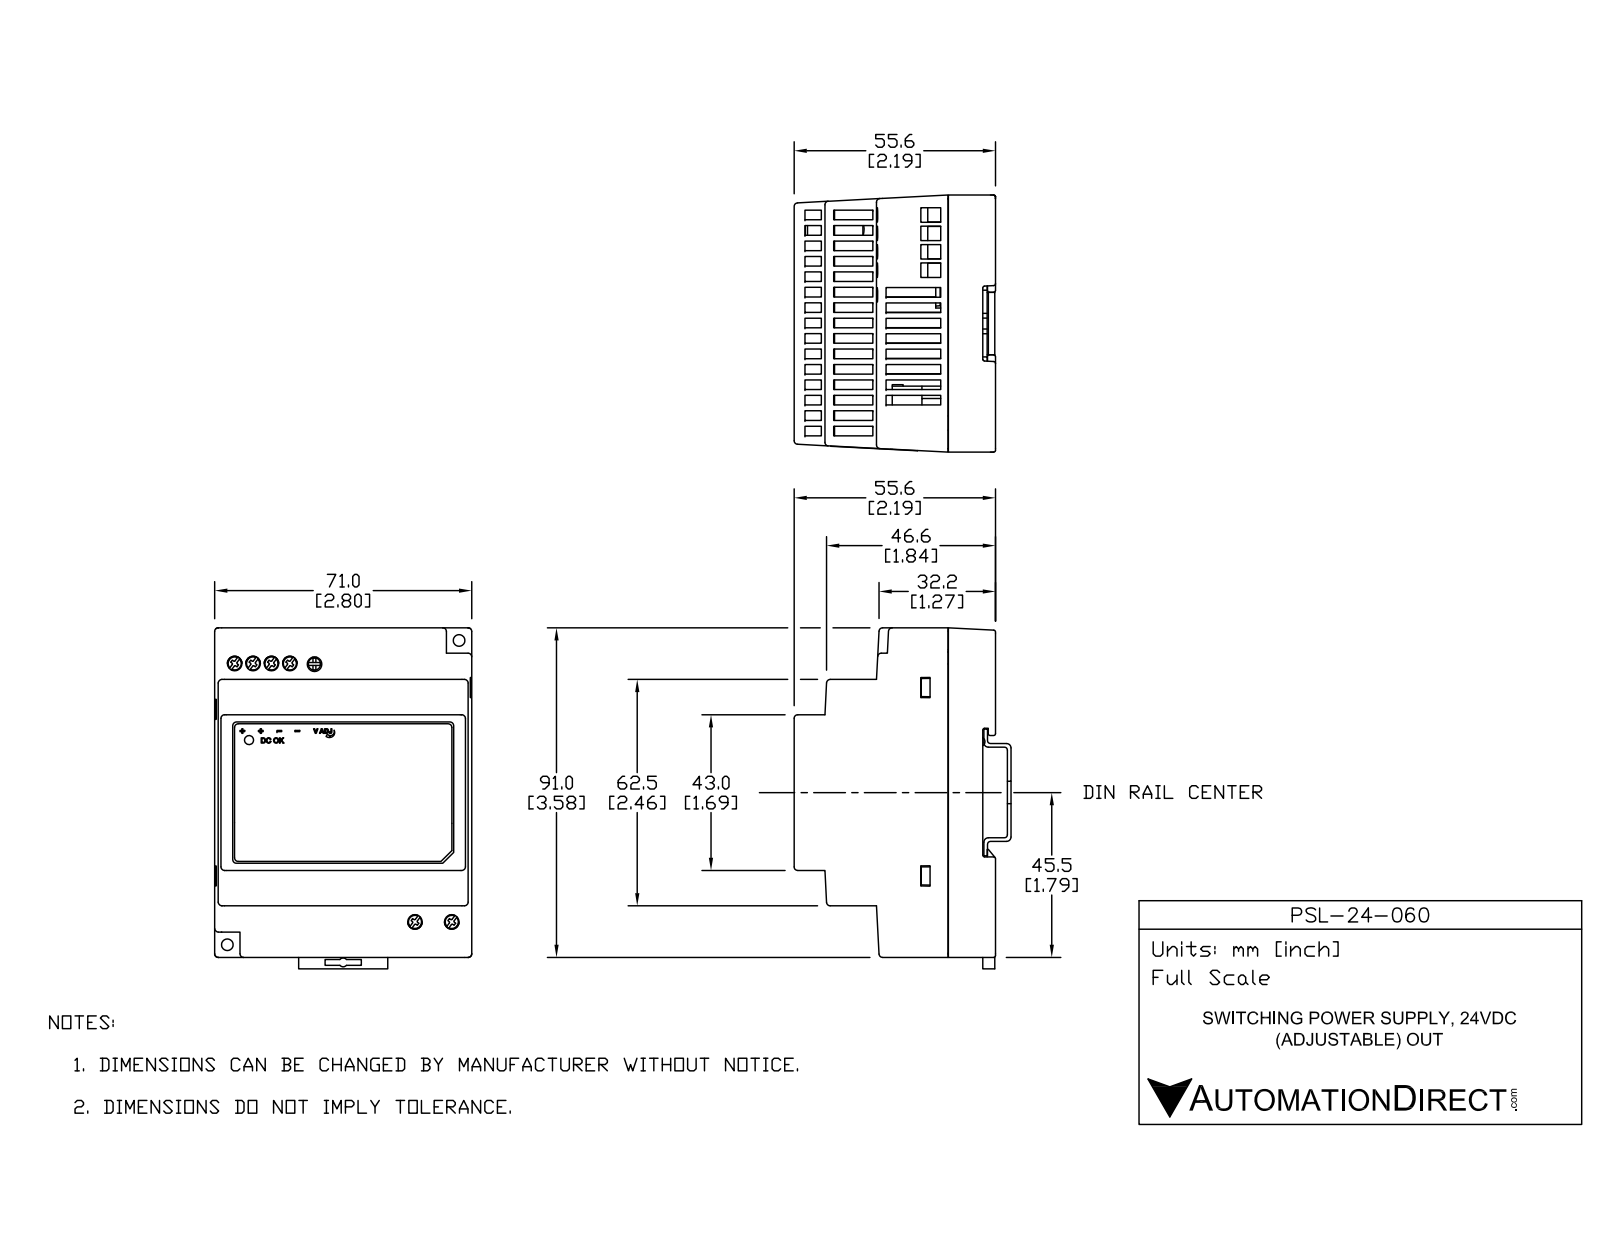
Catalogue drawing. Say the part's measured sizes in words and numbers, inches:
The part is named "PSL-24-060". Its 3-D file was written by "SolidWorks 2017 (AUTOMOTIVE_DESIGN)". It is 5 solids with 957 faces: 662 planar, 193 cylindrical and 102 other. Overall it measures 3.707 by 2.795 by 2.189 inches. Its volume is 3.269 cubic inches and its surface area 95.63 square inches. Round holes: 7 of diameter 0.157, 2 of diameter 0.098, 2 of diameter 0.126, 1 of diameter 0.138. Round bosses or shafts: 1 of diameter 0.156. Partial cylindrical surfaces (rounded edges, fillets, slot ends): 81 of radius 0.02, 47 of radius 0.039, 6 of radius 0.008, 4 of radius 0.079, 2 of radius 0.04, 2 of radius 0.059, 2 of radius 0.128, 2 of radius 0.142. The main face-to-face distances are 0.079, 0.087, 0.079, 1.886, 1.972, 0.541, 2.043, 1.957, 0.071, 0.561. The hole center spacings are 0.2, 0.4, 2.055, 3.315, 3.425, 0.268, 0.277, 0.349.
